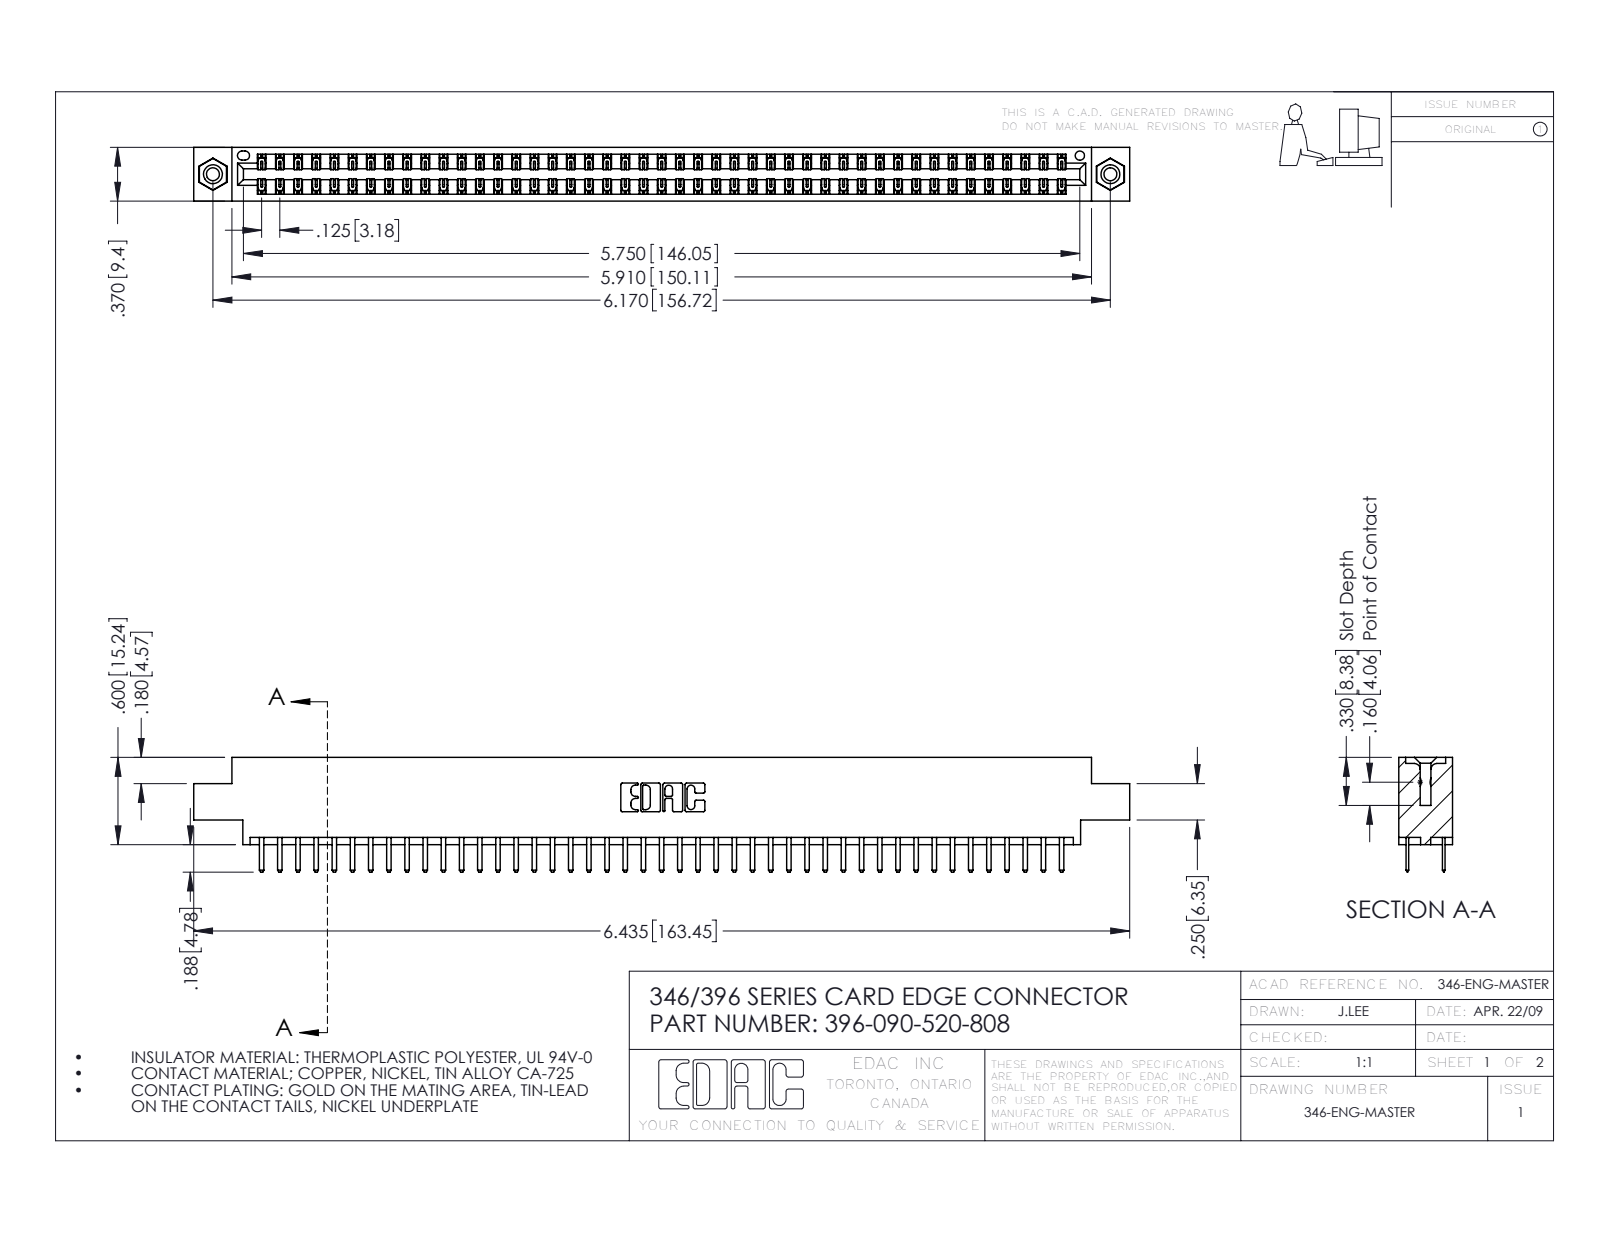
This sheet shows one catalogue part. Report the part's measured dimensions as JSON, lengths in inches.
{"part_name": "345-250-001_345-250-003-102; 396-090-520-808; 346 Part_0.170 Offset - 0.156 Dia-TI; 345-292-001_345-293-120", "step_written_by": "SolidWorks 2016 (CONFIG_CONTROL_DESIGN)", "units": "inches", "bodies": {"solids": 93, "faces": 5226, "planar": 3442, "cylindrical": 1768, "other": 16}, "overall_size": [6.435, 0.788, 0.37], "volume_in3": 0.962, "surface_area_in2": 33.82, "round_holes": [[0.089, 2], [0.125, 2], [0.156, 2], [0.064, 1]], "round_bosses_or_shafts": [[0.155, 2]], "partial_cylinders_radius": [[0.006, 135], [0.01, 94], [0.01, 22], [0.007, 6], [0.031, 6], [0.026, 3], [0.014, 2], [0.022, 2]], "face_to_face_distances": [0.048, 0.322, 0.25, 0.37, 0.275, 0.072, 0.298, 0.025, 0.222, 0.148], "hole_center_spacings": [0.246, 5.961, 6.17]}
